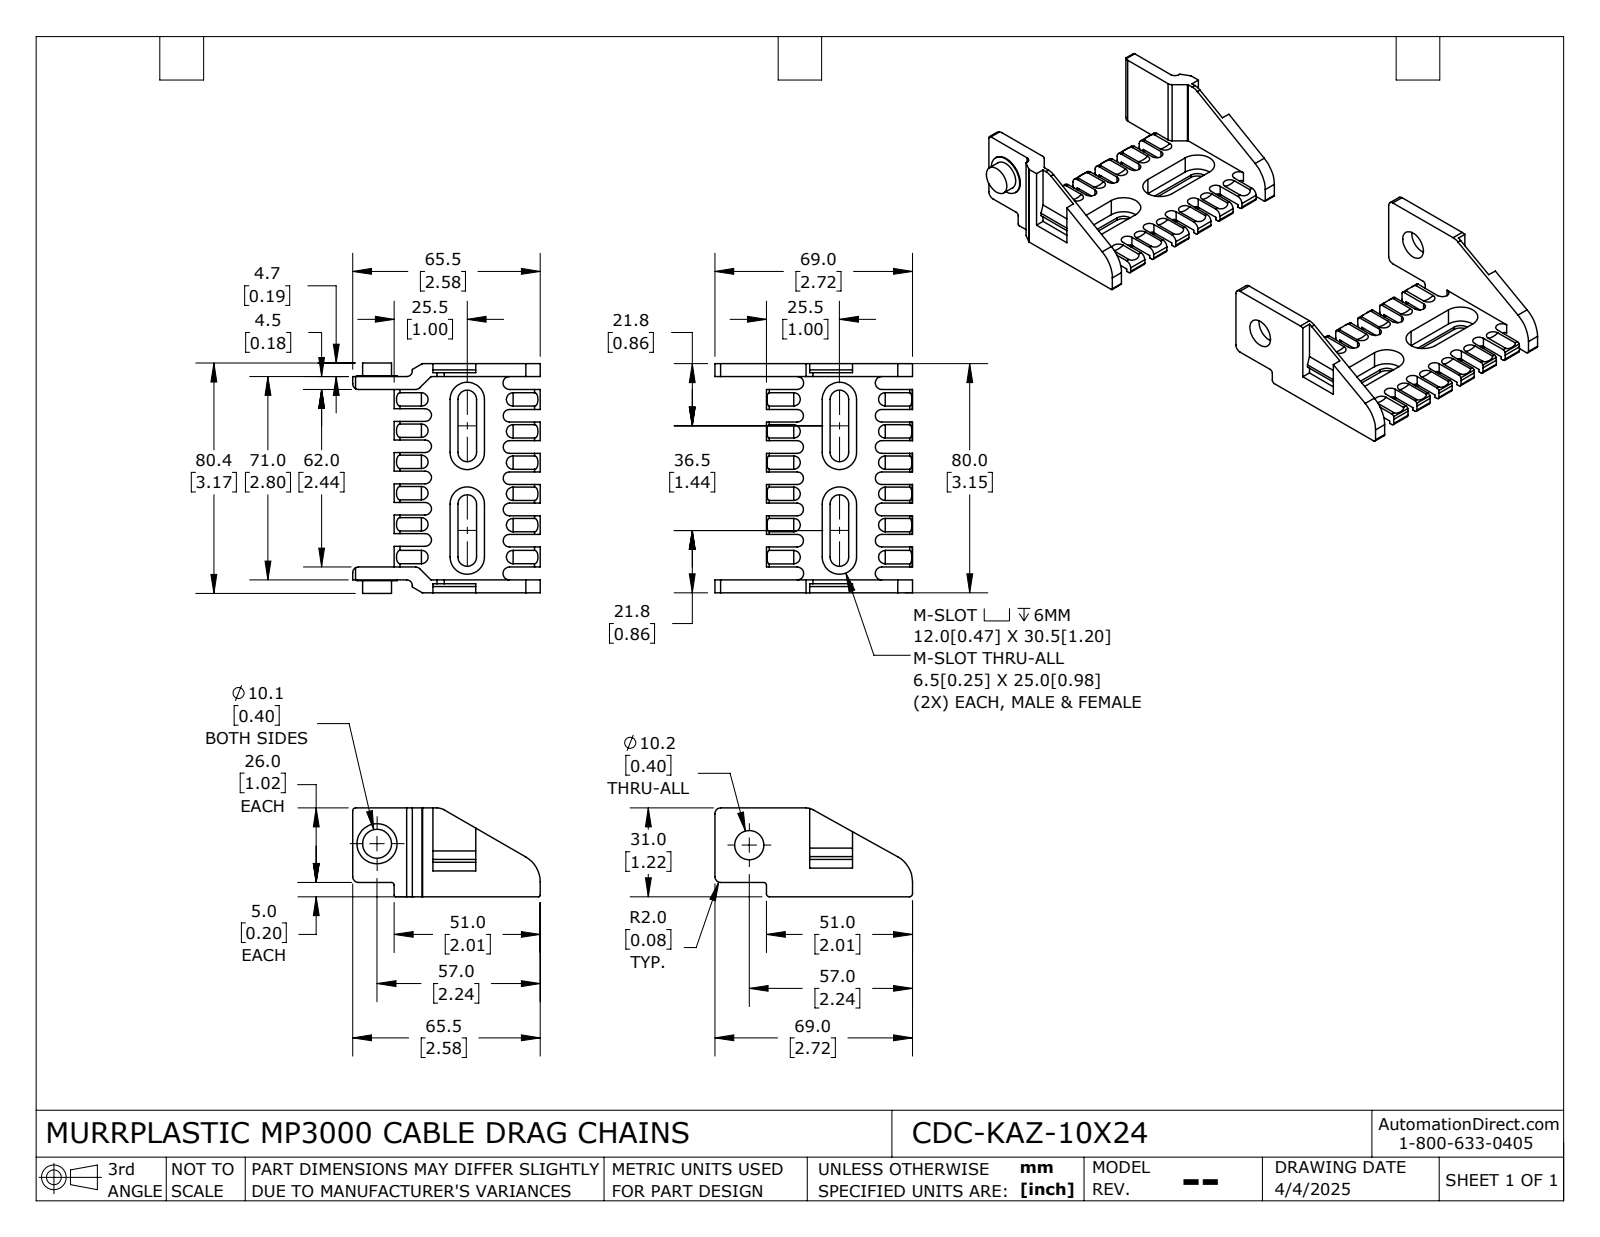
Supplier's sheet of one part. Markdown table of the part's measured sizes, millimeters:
| quantity | value |
| --- | --- |
| part name | CDC-KAZ-10X24 |
| STEP written by | SolidWorks 2024 (AUTOMOTIVE_DESIGN) |
| units | millimeters |
| bodies | 2 solids, 481 faces (258 planar, 199 cylindrical, 24 other) |
| overall size | 195.5 × 80.4 × 31 |
| volume | 51 111 mm³ |
| surface area | 32 568 mm² |
| round holes (diameter × count) | 10.2 × 1 |
| round bosses / shafts (diameter × count) | 14 × 1, 10.1 × 1 |
| partial cylindrical surfaces (radius × count) | 2.2 × 20, 1 × 15, 2 × 13, 7 × 12, 3.25 × 8, 6 × 8, 2.25 × 6, 0.5 × 4 |
| main face-to-face distances | 4.5, 75.5, 71, 7, 3.5, 80, 9, 66.5, 2.5, 1 |
